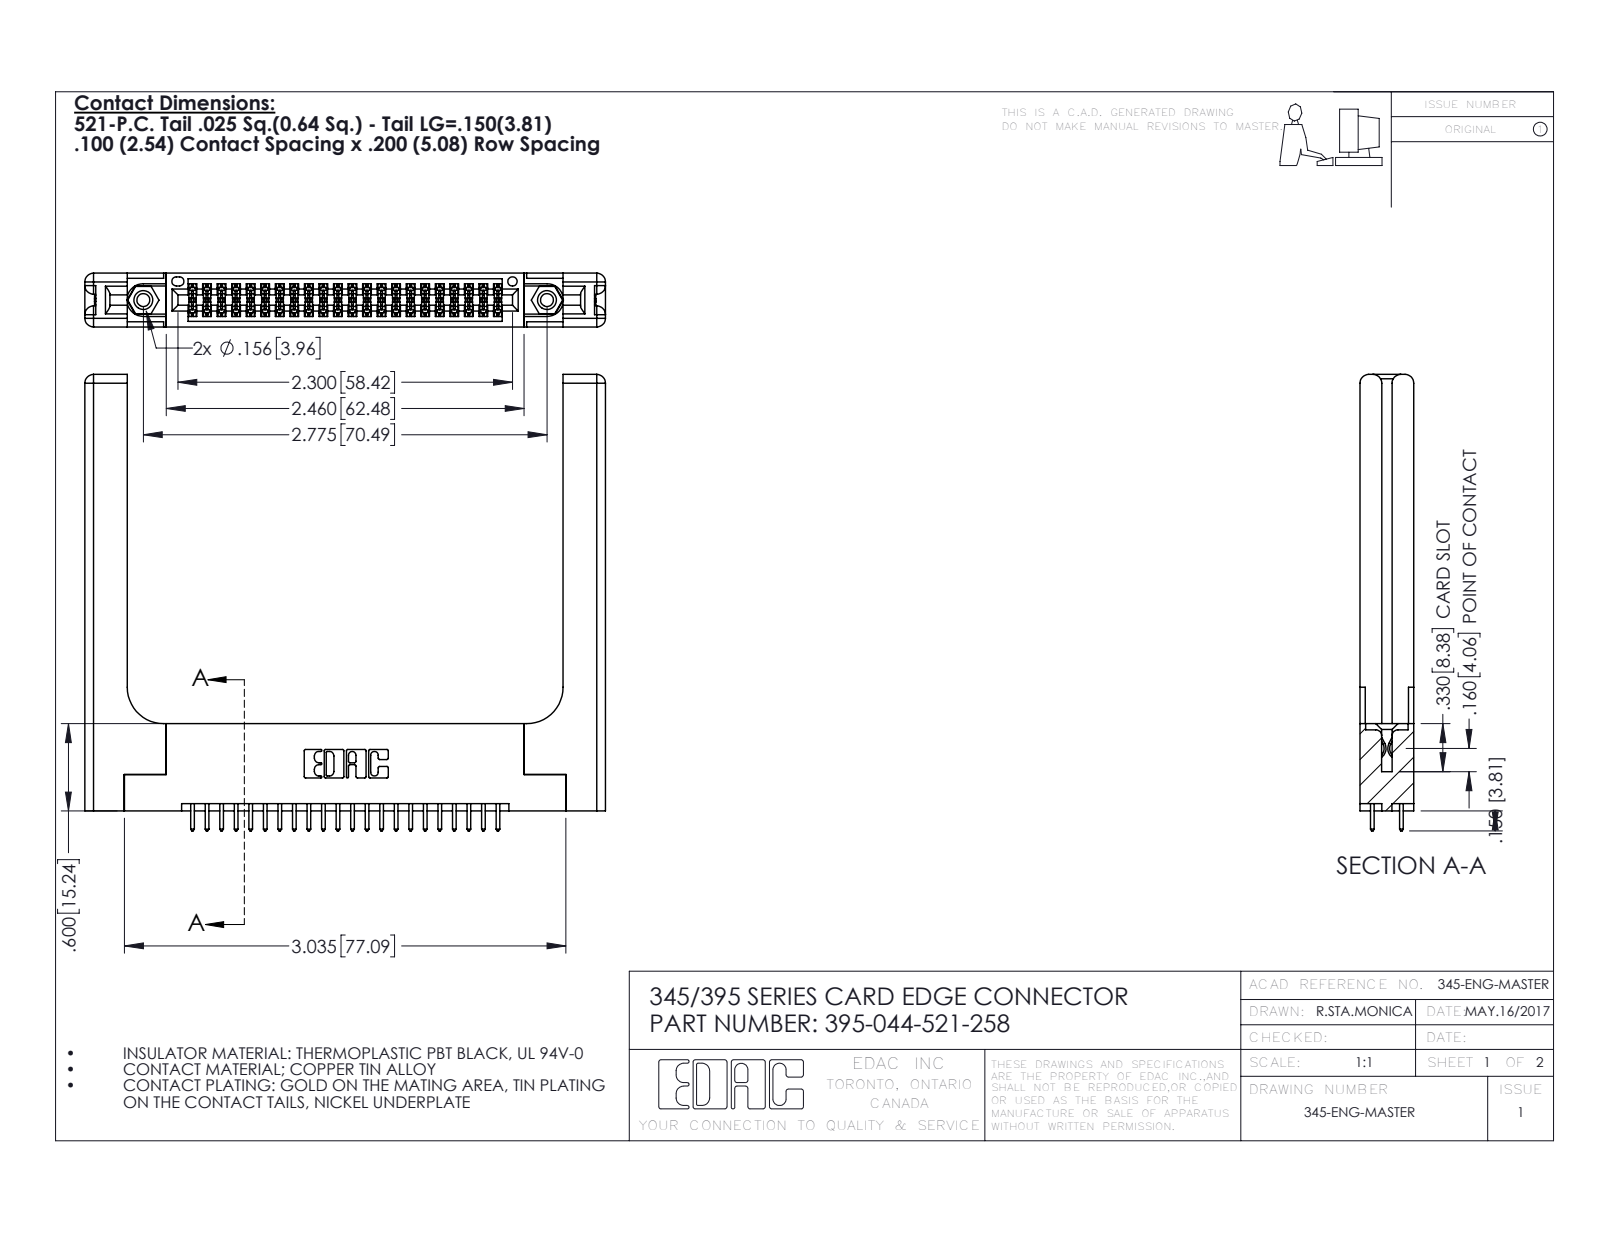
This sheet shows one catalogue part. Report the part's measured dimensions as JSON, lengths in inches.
{"part_name": "345-250-001_345-250-001-102; 345 Part_Flush Mounting Lugs - 0.156 Dia-TH; 345-292-001_345-293-121; 395-044-521-258 (+1 more)", "step_written_by": "SolidWorks 2016 (CONFIG_CONTROL_DESIGN)", "units": "inches", "bodies": {"solids": 49, "faces": 2582, "planar": 1680, "cylindrical": 842, "other": 60}, "overall_size": [3.579, 3.137, 0.37], "volume_in3": 1.044, "surface_area_in2": 26.83, "round_holes": [[0.089, 2], [0.125, 2], [0.156, 2], [0.064, 1]], "round_bosses_or_shafts": [[0.155, 2]], "partial_cylinders_radius": [[0.006, 66], [0.01, 44], [0.01, 22], [0.06, 16], [0.007, 6], [0.031, 6], [0.026, 3], [0.014, 2]], "face_to_face_distances": [0.37, 0.072, 0.298, 0.2, 0.15, 0.148, 0.098, 0.272, 0.025, 0.225], "hole_center_spacings": [0.27, 2.541, 2.775]}
